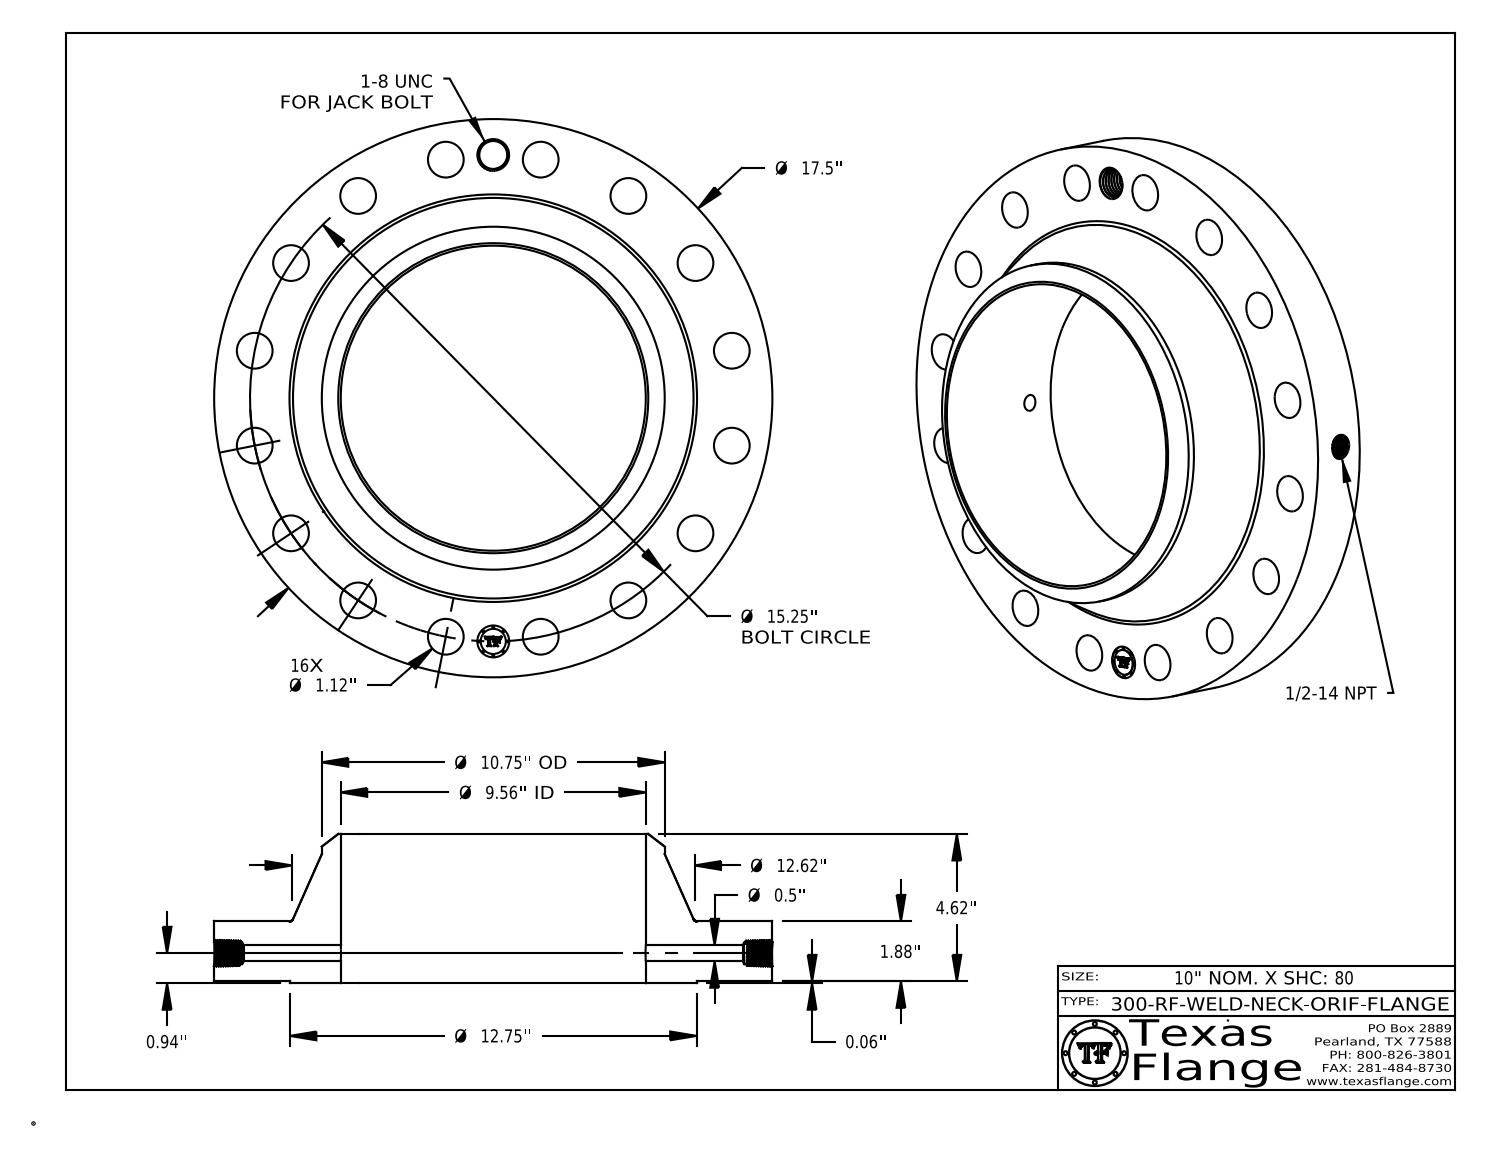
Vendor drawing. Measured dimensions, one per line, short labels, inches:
name: 300-RF-WELD-NECK
written by: CATIA V5 STEP AP214 (AUTOMOTIVE_DESIGN)
unit: in
bodies: 1 solid, 787 faces (369 planar, 109 cylindrical, 309 other)
size: 17.5 × 17.5 × 4.68
volume: 371.5 in³; area: 742.4 in²
holes: 16× ⌀1.12, 1× ⌀0.5, 1× ⌀0.672, 1× ⌀0.875, 1× ⌀1, 1× ⌀9.562
bosses: 8× ⌀0.061, 1× ⌀17.5, 1× ⌀12.75, 1× ⌀10.75, 1× ⌀0.788
face distances: 1.88, 0.06, 1.94, 4.68, 4.62, 2.74, 0.015, 1.925, 1.865, 2.755
hole spacings: 5.836, 7.625, 10.783, 14.089, 14.957, 2.975, 2.975, 8.472
